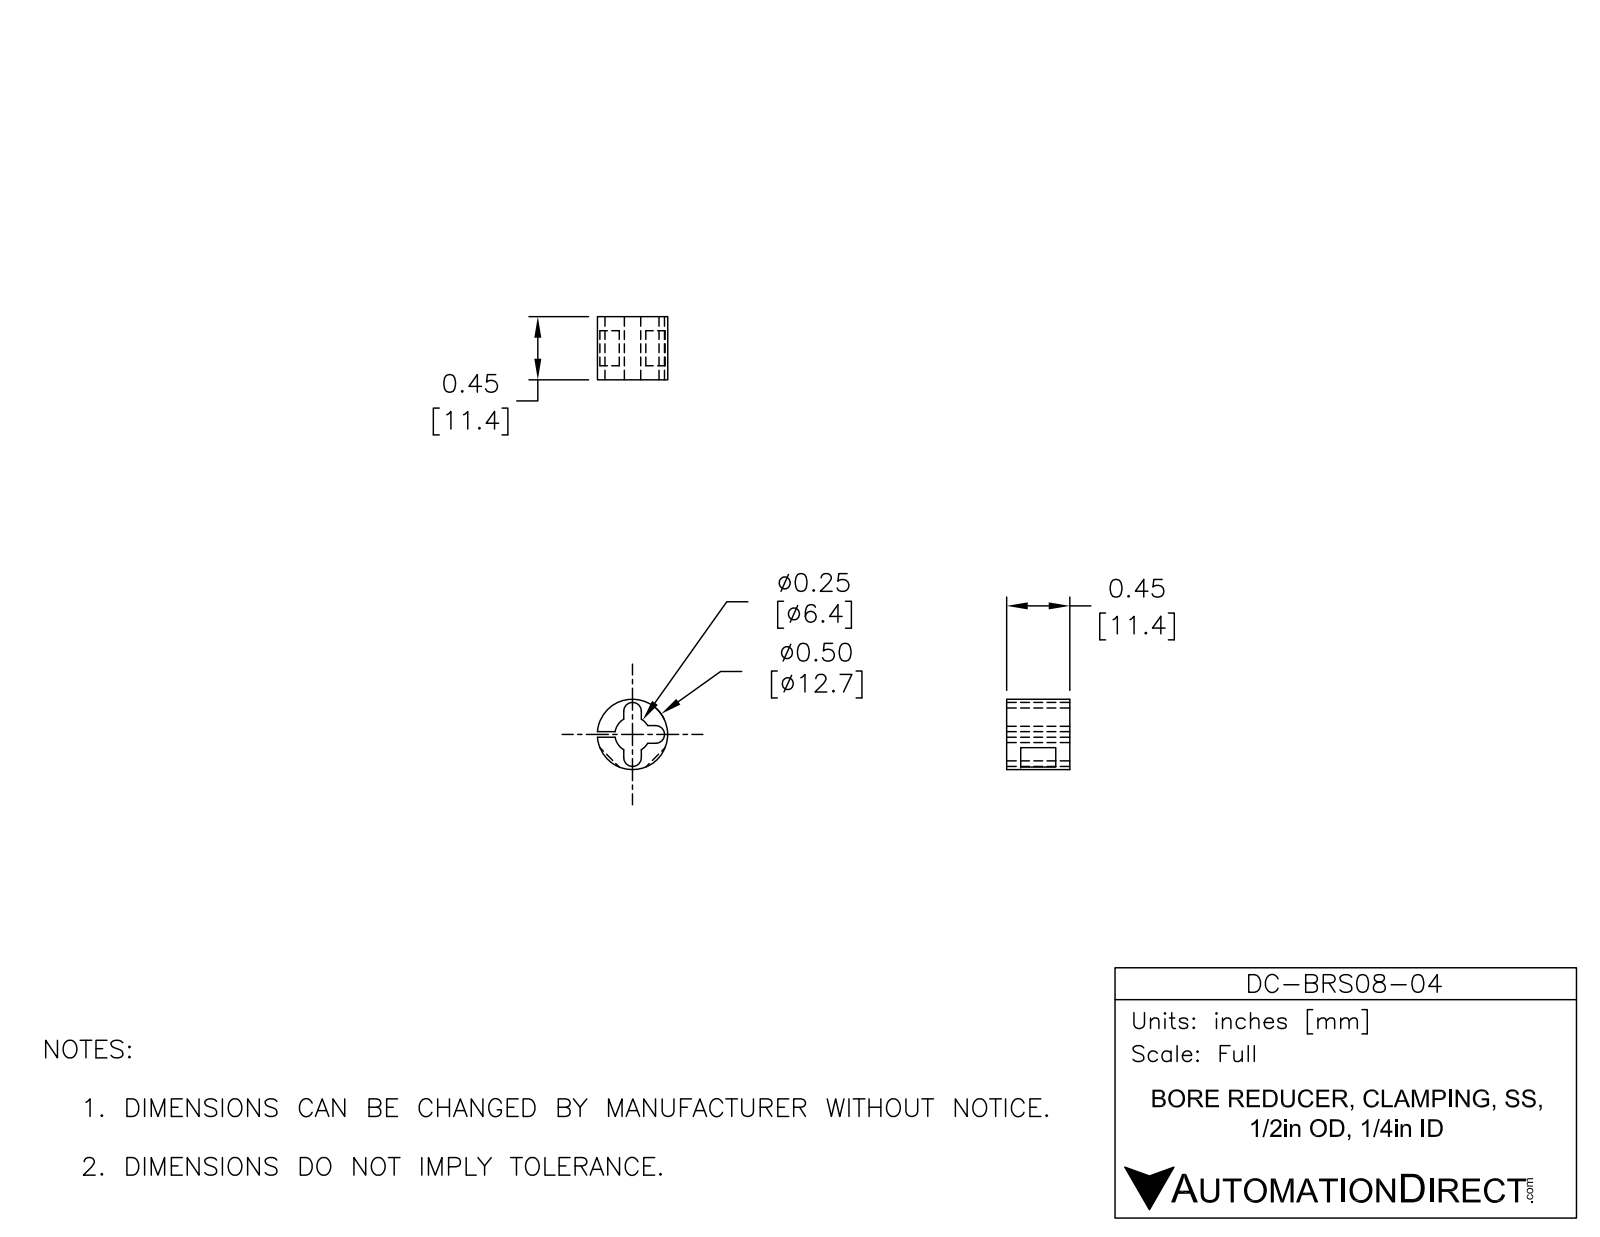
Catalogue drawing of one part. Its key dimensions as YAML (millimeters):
part_name: "DC-BRS08-04"
step_written_by: "SolidWorks 2015 (AUTOMOTIVE_DESIGN)"
units: millimeters
bodies: {solids: 1, faces: 27, planar: 16, cylindrical: 11, other: 0}
overall_size: [12.7, 12.68, 11.4]
volume: 765
surface_area: 1030
round_bosses_or_shafts:
  - {diameter: 12.7, count: 1}
partial_cylinders:
  - {radius: 1.59, count: 3}
  - {radius: 3.17, count: 1}
face_to_face_distances: [11.4, 3.18, 1.02, 1.08, 2.1, 2.54, 8.86, 6.32]
